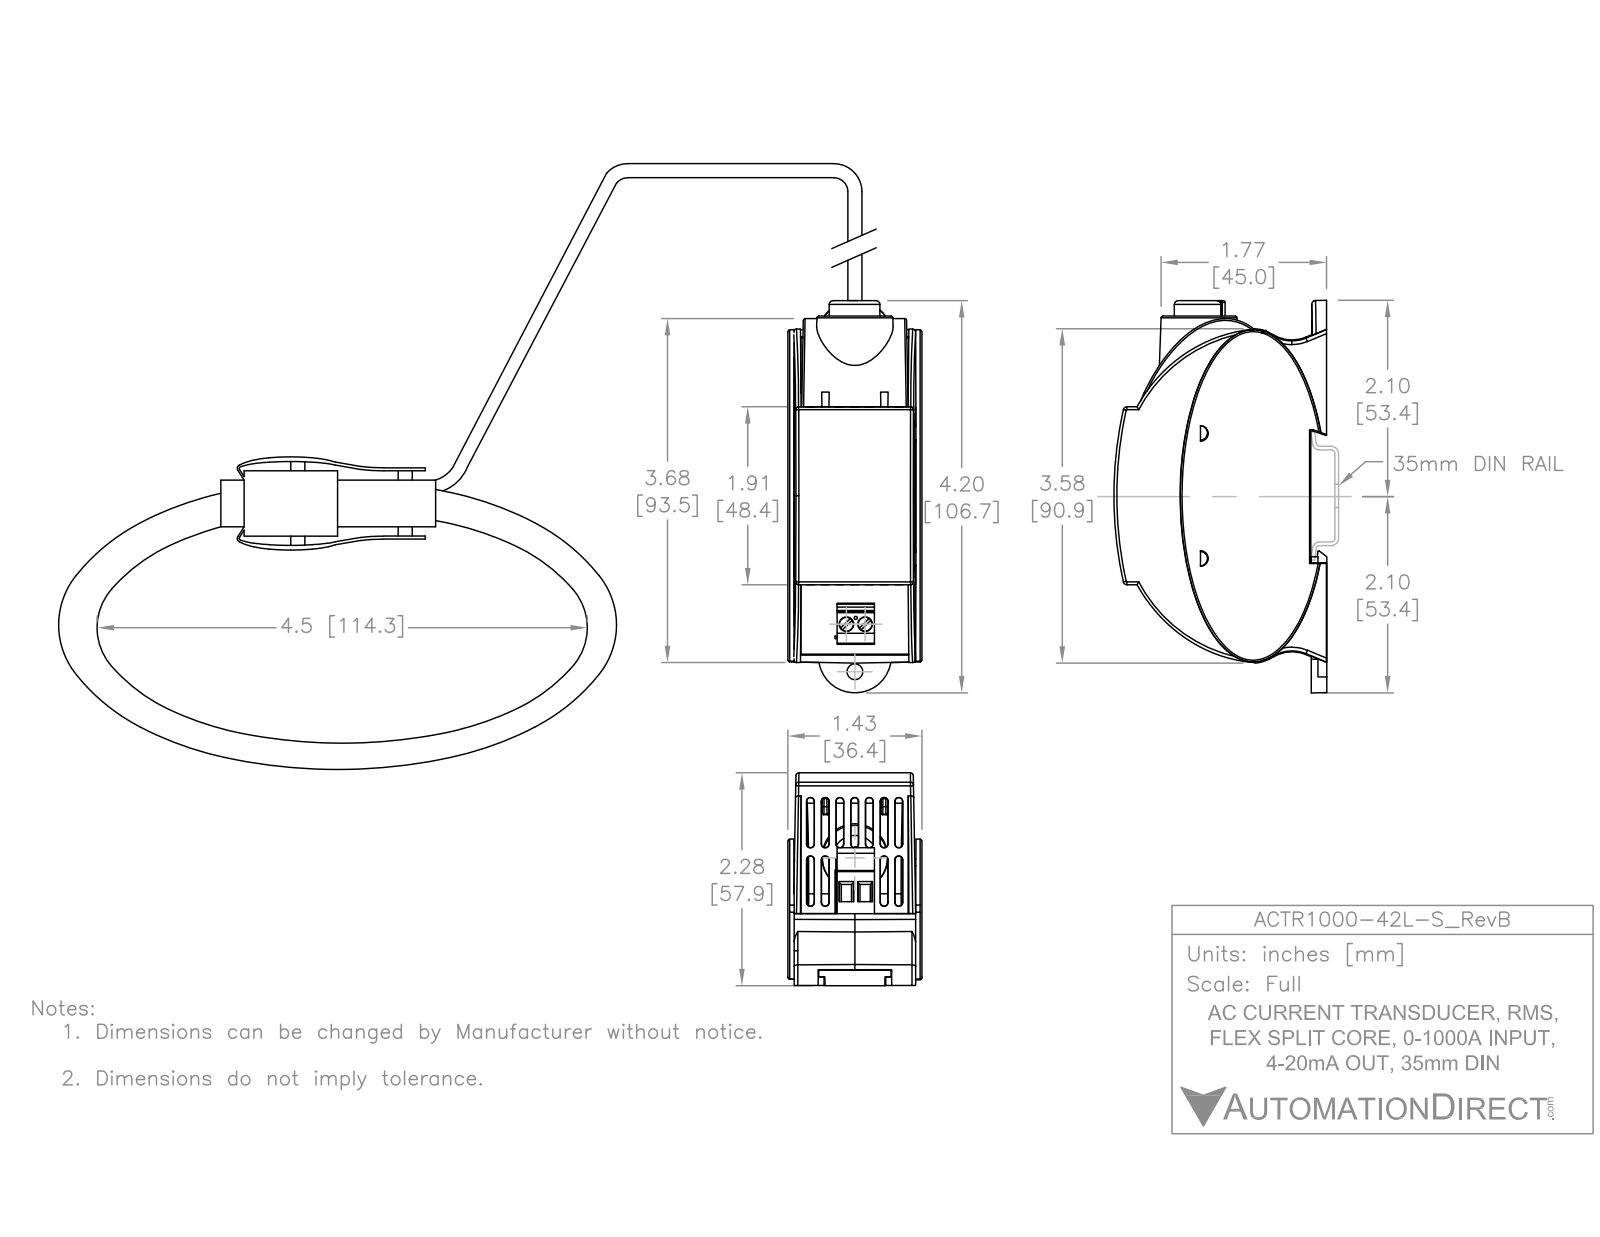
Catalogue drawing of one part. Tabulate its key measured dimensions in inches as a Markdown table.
| quantity | value |
| --- | --- |
| part name | ACTR1000-42L-S |
| STEP written by | SolidWorks 2021 (AUTOMOTIVE_DESIGN) |
| units | inches |
| bodies | 8 solids, 723 faces (379 planar, 123 cylindrical, 221 other) |
| overall size | 4.203 × 2.298 × 1.46 |
| volume | 3.122 in³ |
| surface area | 82.28 in² |
| round holes (diameter × count) | 0.157 × 2 |
| round bosses / shafts (diameter × count) | 0.15 × 2, 0.543 × 1, 0.018 × 1 |
| partial cylindrical surfaces (radius × count) | 0.02 × 22, 0.006 × 10, 0.01 × 10, 0.02 × 10, 0.039 × 10, 0.026 × 8, 0.008 × 4, 0.032 × 4 |
| main face-to-face distances | 1.435, 0.064, 0.436, 0.5, 0.059, 1.267, 1.261, 0.266, 0.702, 0.766 |
| hole center spacings | 0.2 |
